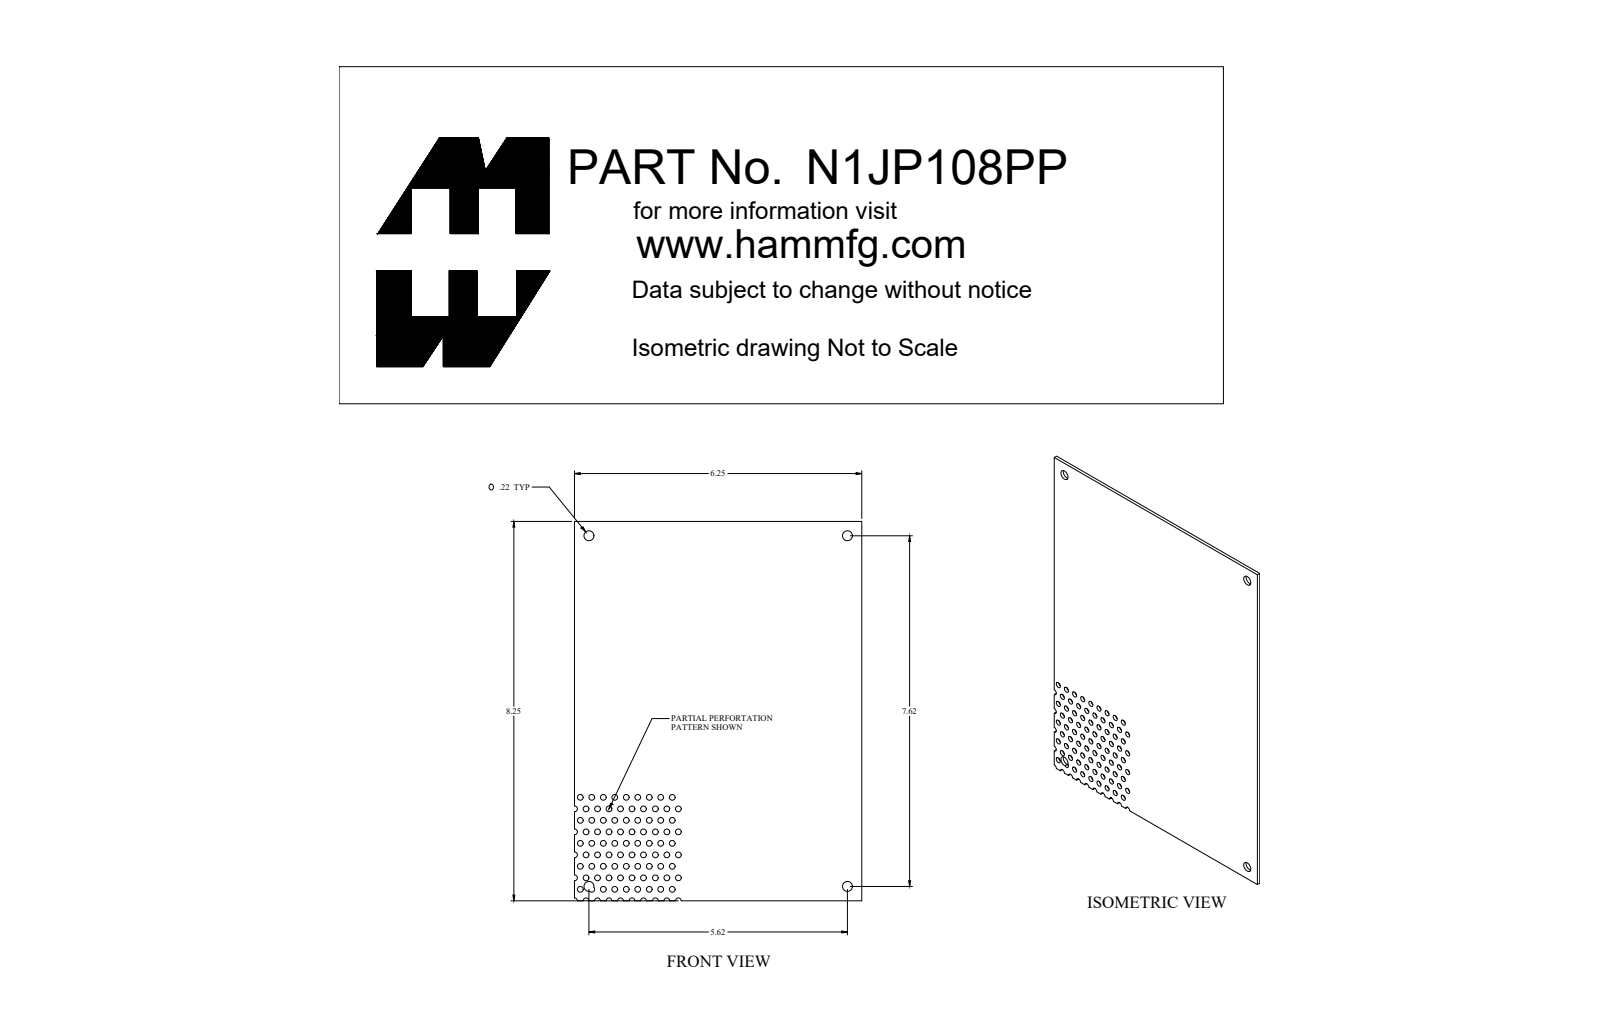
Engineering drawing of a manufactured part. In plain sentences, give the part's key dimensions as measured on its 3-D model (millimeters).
The part is named "N1JP108PP". Its 3-D file was written by "SolidWorks 2018 (AUTOMOTIVE_DESIGN)". It is 1 solid with 203 faces: 19 planar, 184 cylindrical and 0 other. Overall it measures 209.6 by 158.8 by 1.8 millimeters. Its volume is 59 400 cubic millimeters and its surface area 67 940 square millimeters. Round holes: 58 of diameter 3.2, 22 of diameter 3.2, 4 of diameter 5.5. Partial cylindrical surfaces (rounded edges, fillets, slot ends): 8 of radius 1.6, 7 of radius 1.6. The main face-to-face distances are 1.8, 158.8, 209.6. The hole center spacings are 12.7, 6.4, 14.2, 18, 19.1, 7.1, 22.9, 7.1.
